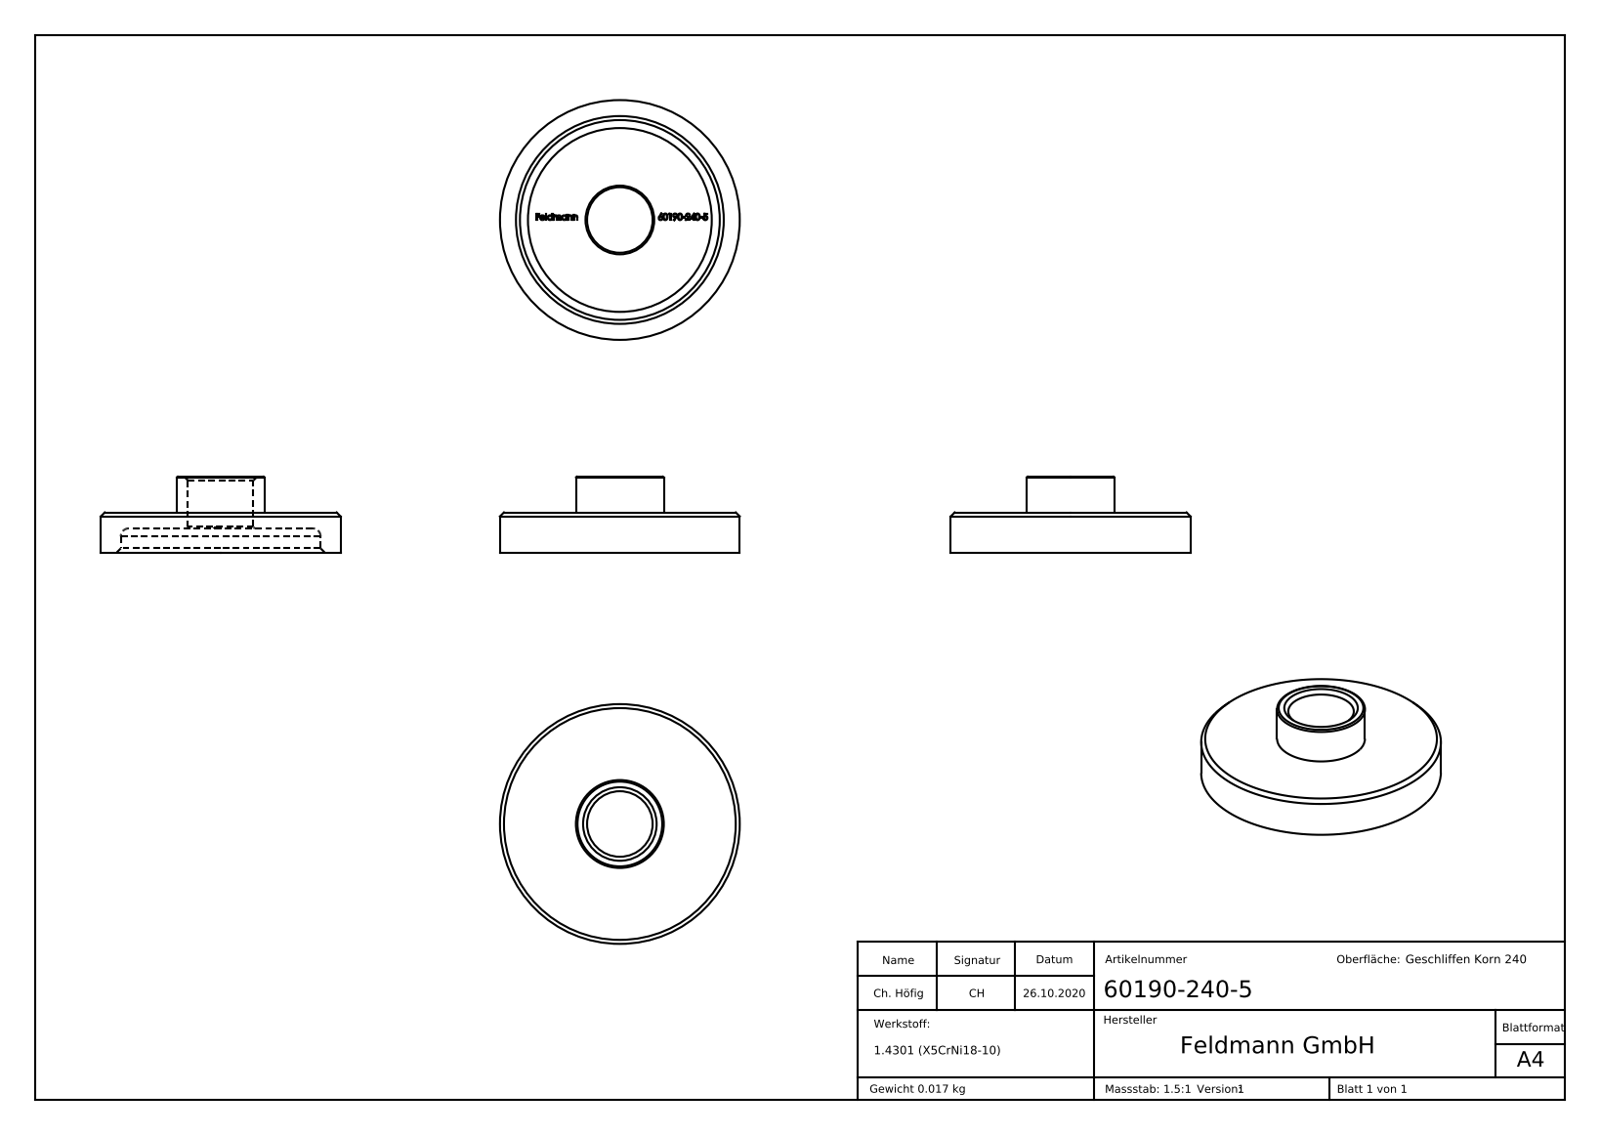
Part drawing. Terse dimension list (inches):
name: 60190-240-5
written by: SolidWorks 2018 (CONFIG_CONTROL_DESIGN)
unit: in
bodies: 1 solid, 258 faces (131 planar, 8 cylindrical, 119 other)
size: 1.181 × 1.181 × 0.374
volume: 0.13 in³; area: 3.483 in²
holes: 1× ⌀0.323, 1× ⌀0.984
bosses: 1× ⌀1.181, 1× ⌀0.433
face distances: 0.079, 0.118, 0.197, 0.374, 0.256, 0.177, 0.122, 0.075, 0.252, 0.07
